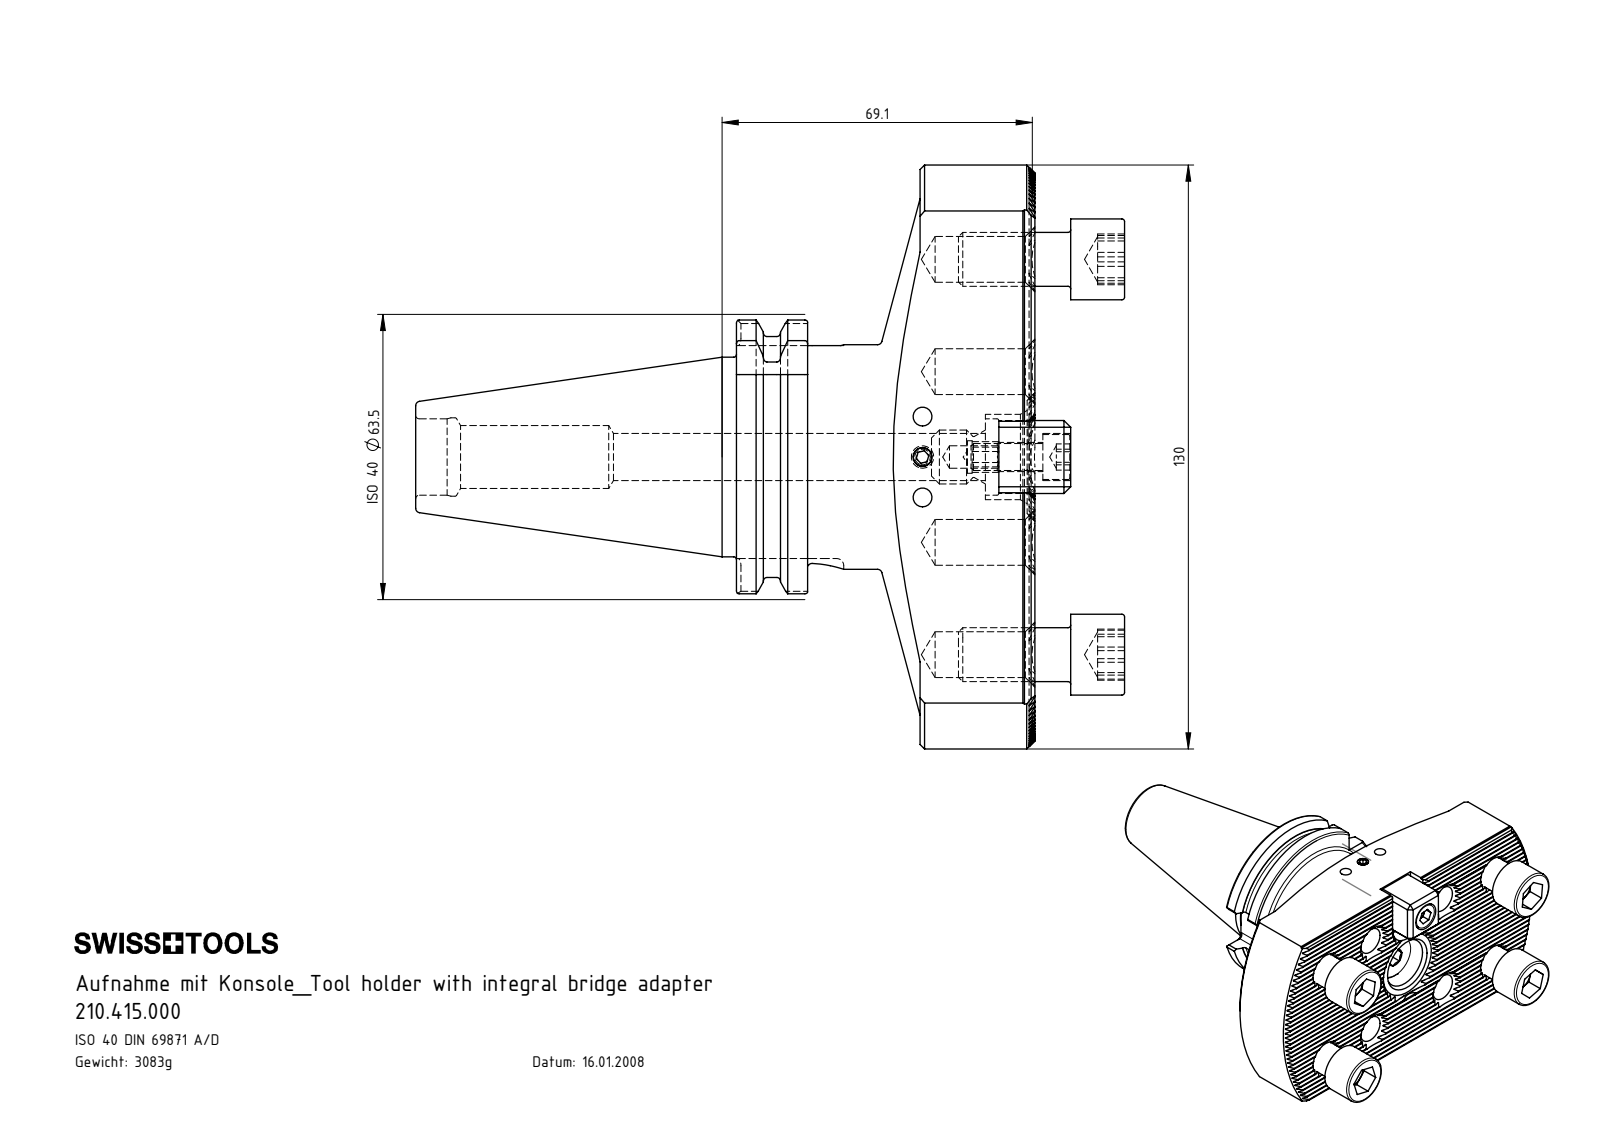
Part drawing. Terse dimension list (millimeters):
name: 210.415.000; Ko1-ER1.001.016_A; ISO 4762 M6 x 16; ISO 4762 M12 x 25 (+3 more)
written by: SolidWorks 2017 (CONFIG_CONTROL_DESIGN)
unit: mm
bodies: 10 solids, 886 faces (502 planar, 210 cylindrical, 174 other)
size: 157.9 × 130 × 70
volume: 392 696 mm³; area: 72 489 mm²
holes: 8× ⌀10.2, 3× ⌀4.2, 2× ⌀10.5, 1× ⌀5, 1× ⌀6.5, 1× ⌀7.24, 1× ⌀14, 1× ⌀17, 1× ⌀17.45, 1× ⌀19
bosses: 5× ⌀12, 4× ⌀18, 1× ⌀50, 1× ⌀44.45, 1× ⌀10, 1× ⌀6, 1× ⌀5
rounds: 34× R0.14, 8× R1.6, 1× R7.95, 1× R8, 1× R8.05, 1× R28, 1× R31.75, 1× R65
face distances: 1.73, 17.32, 70, 8.66, 3.46, 5.2, 6.93, 15.59, 19.05, 3.47
hole spacings: 25, 27.59, 40, 47.17, 48.33, 63, 74.63, 9
